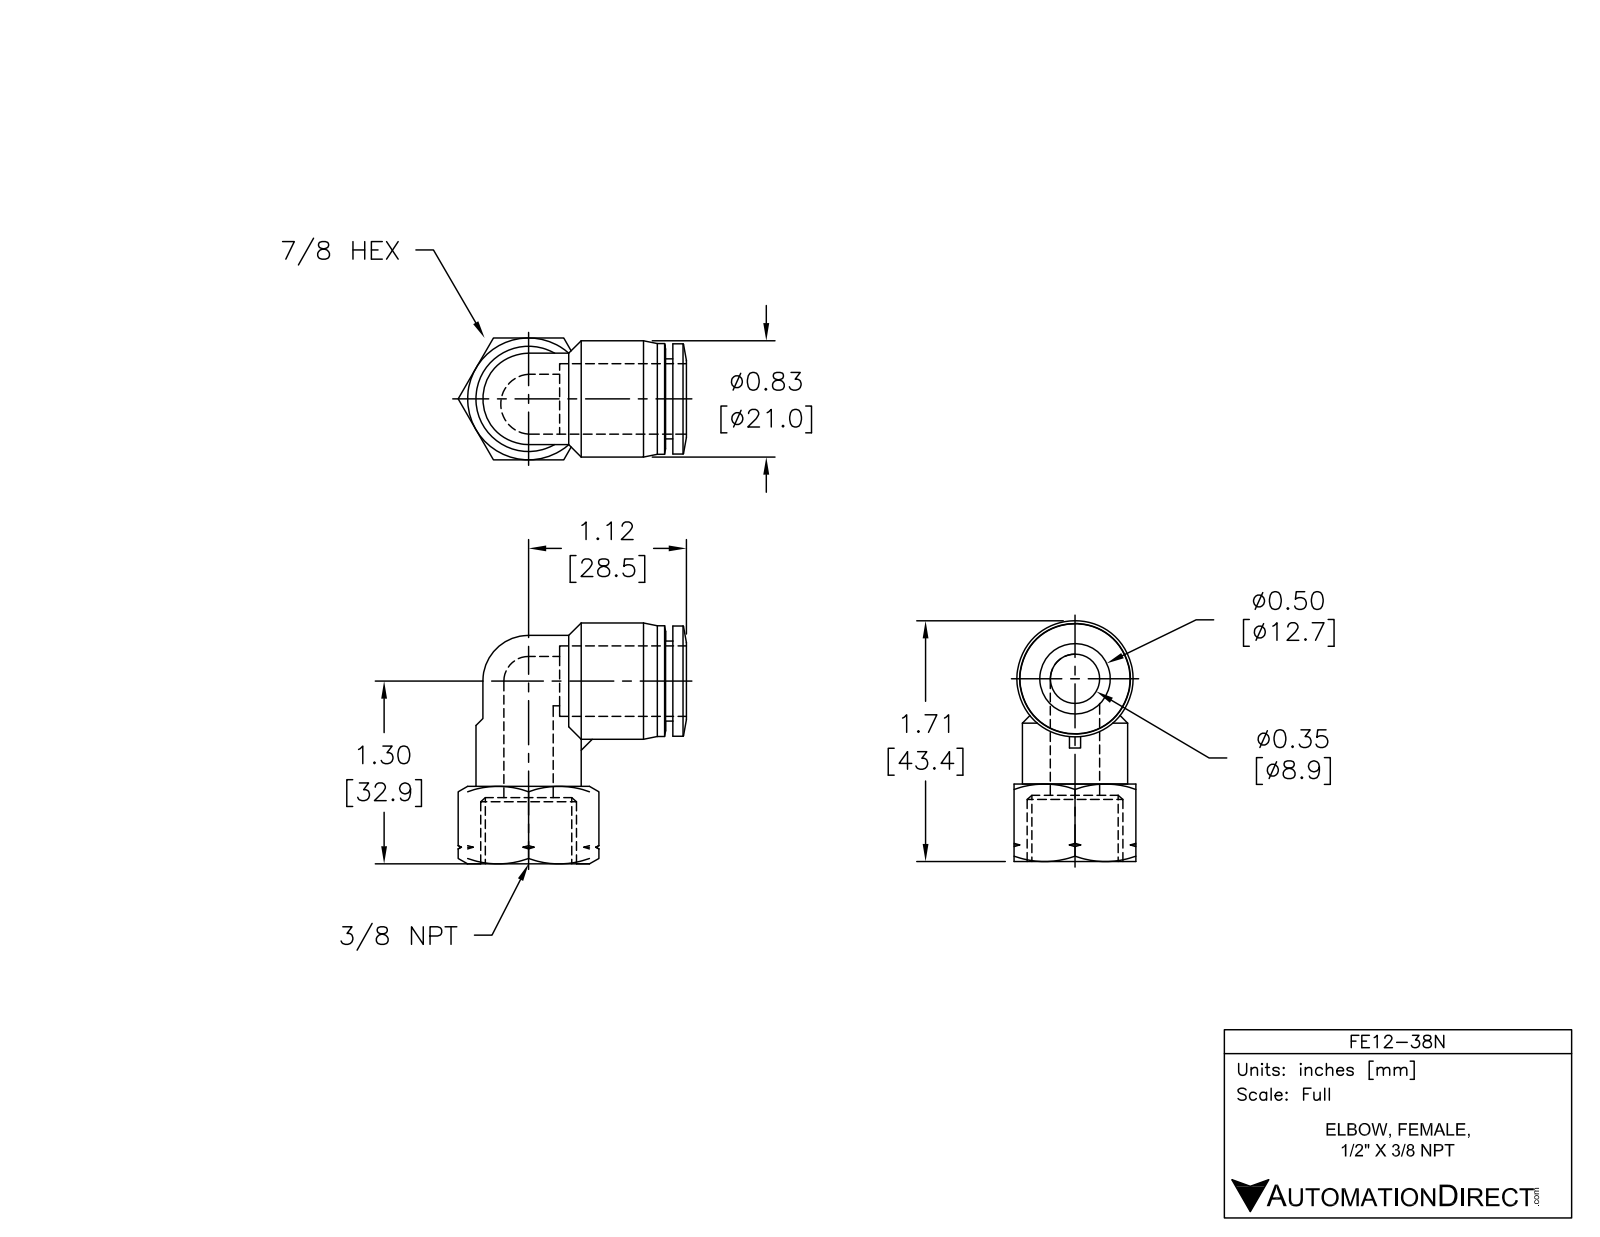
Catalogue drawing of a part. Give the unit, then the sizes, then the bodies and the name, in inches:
Units: inches
Overall size (bounding box): 1.713 × 1.612 × 0.866
Round holes (diameter × count): ⌀0.354 ×2, ⌀0.51 ×1
Round bosses / shafts (diameter × count): ⌀0.65 ×2, ⌀0.827 ×1, ⌀0.787 ×1, ⌀0.783 ×1, ⌀0.748 ×1, ⌀0.569 ×1
Main face-to-face distances: 0.866, 0.472, 0.079, 0.551, 0.051, 0.762, 0.813, 0.394
Volume: 0.696 in³ · Surface area: 10.93 in²
Bodies: 1 solid, 84 faces (15 planar, 20 cylindrical, 49 other)
Part name (STEP PRODUCT): FE12-38N
STEP written by: SolidWorks 2015 (AUTOMOTIVE_DESIGN)
